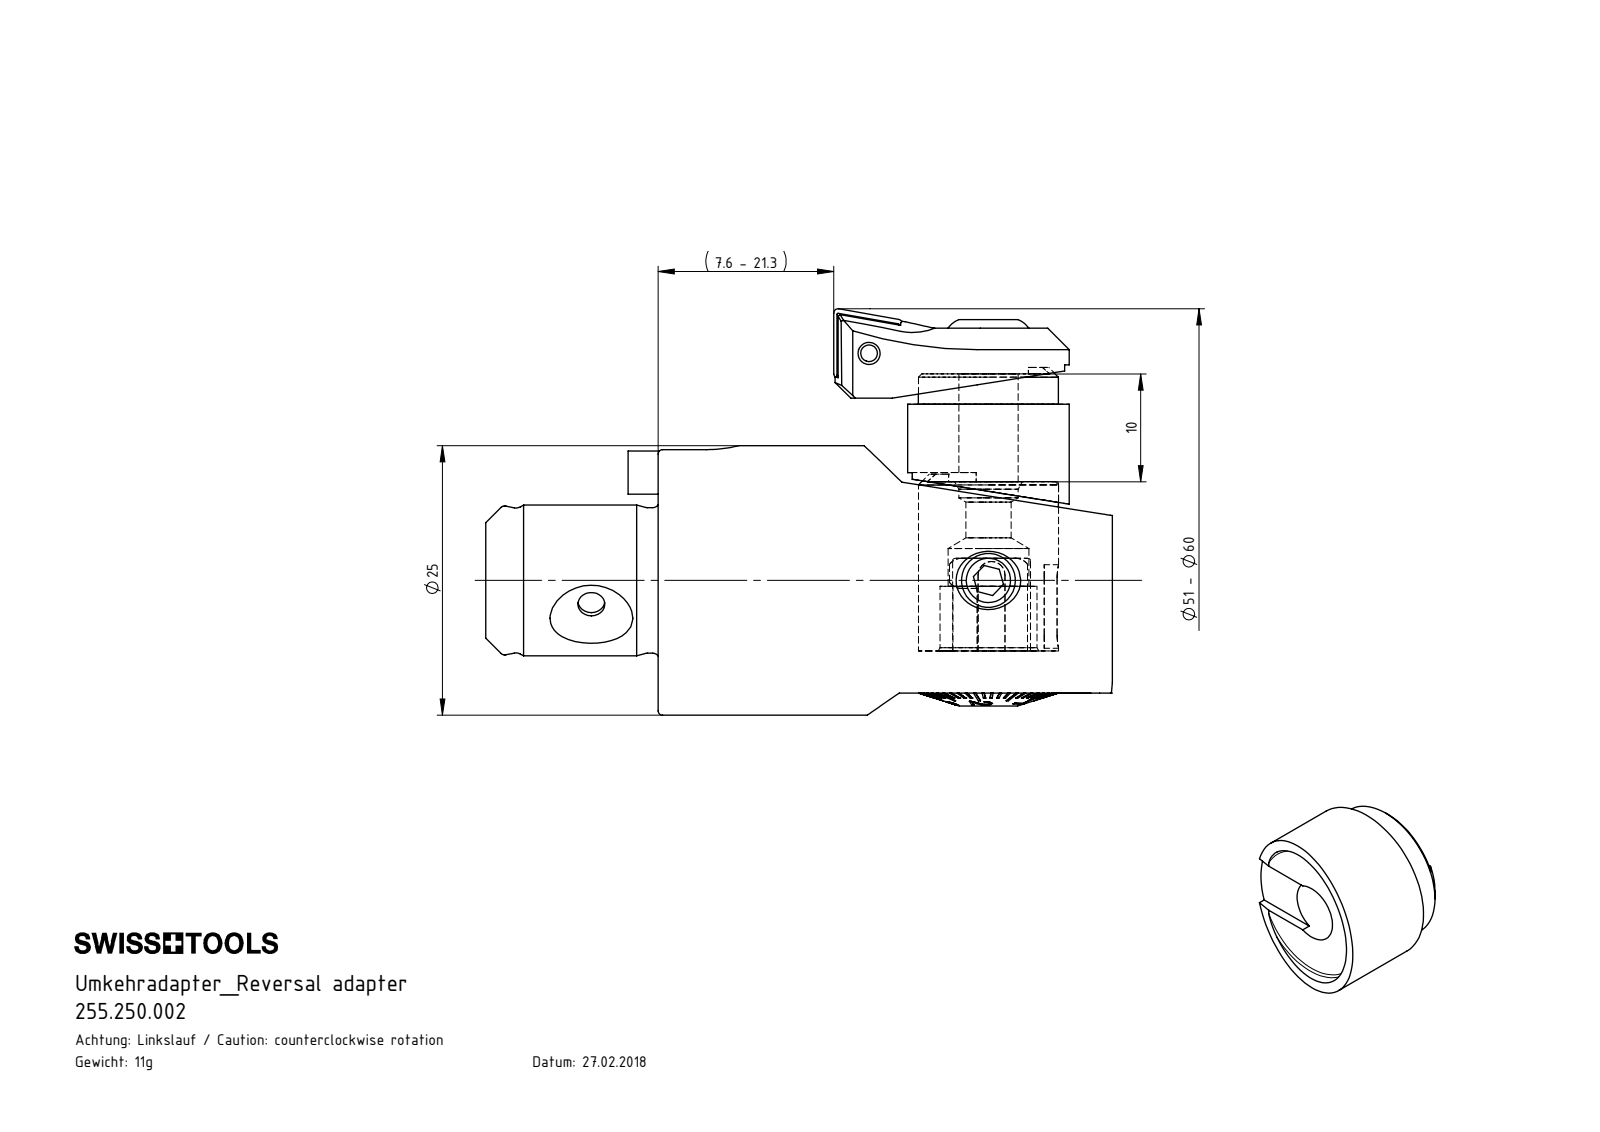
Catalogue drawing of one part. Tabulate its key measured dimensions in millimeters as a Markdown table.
| quantity | value |
| --- | --- |
| part name | F25-U00.001.010_B; 255.250.002 |
| STEP written by | SolidWorks 2017 (CONFIG_CONTROL_DESIGN) |
| units | millimeters |
| bodies | 1 solid, 27 faces (11 planar, 11 cylindrical, 5 other) |
| overall size | 15 × 15 × 12.68 |
| volume | 1 429 mm³ |
| surface area | 1 009 mm² |
| round holes (diameter × count) | 5.5 × 1, 13 × 1 |
| round bosses / shafts (diameter × count) | 15 × 1 |
| partial cylindrical surfaces (radius × count) | 0.5 × 2 |
| main face-to-face distances | 10, 2.8, 7.2, 9.15, 6.35, 0.85, 0.6, 3.4, 9.75, 10.6 |
